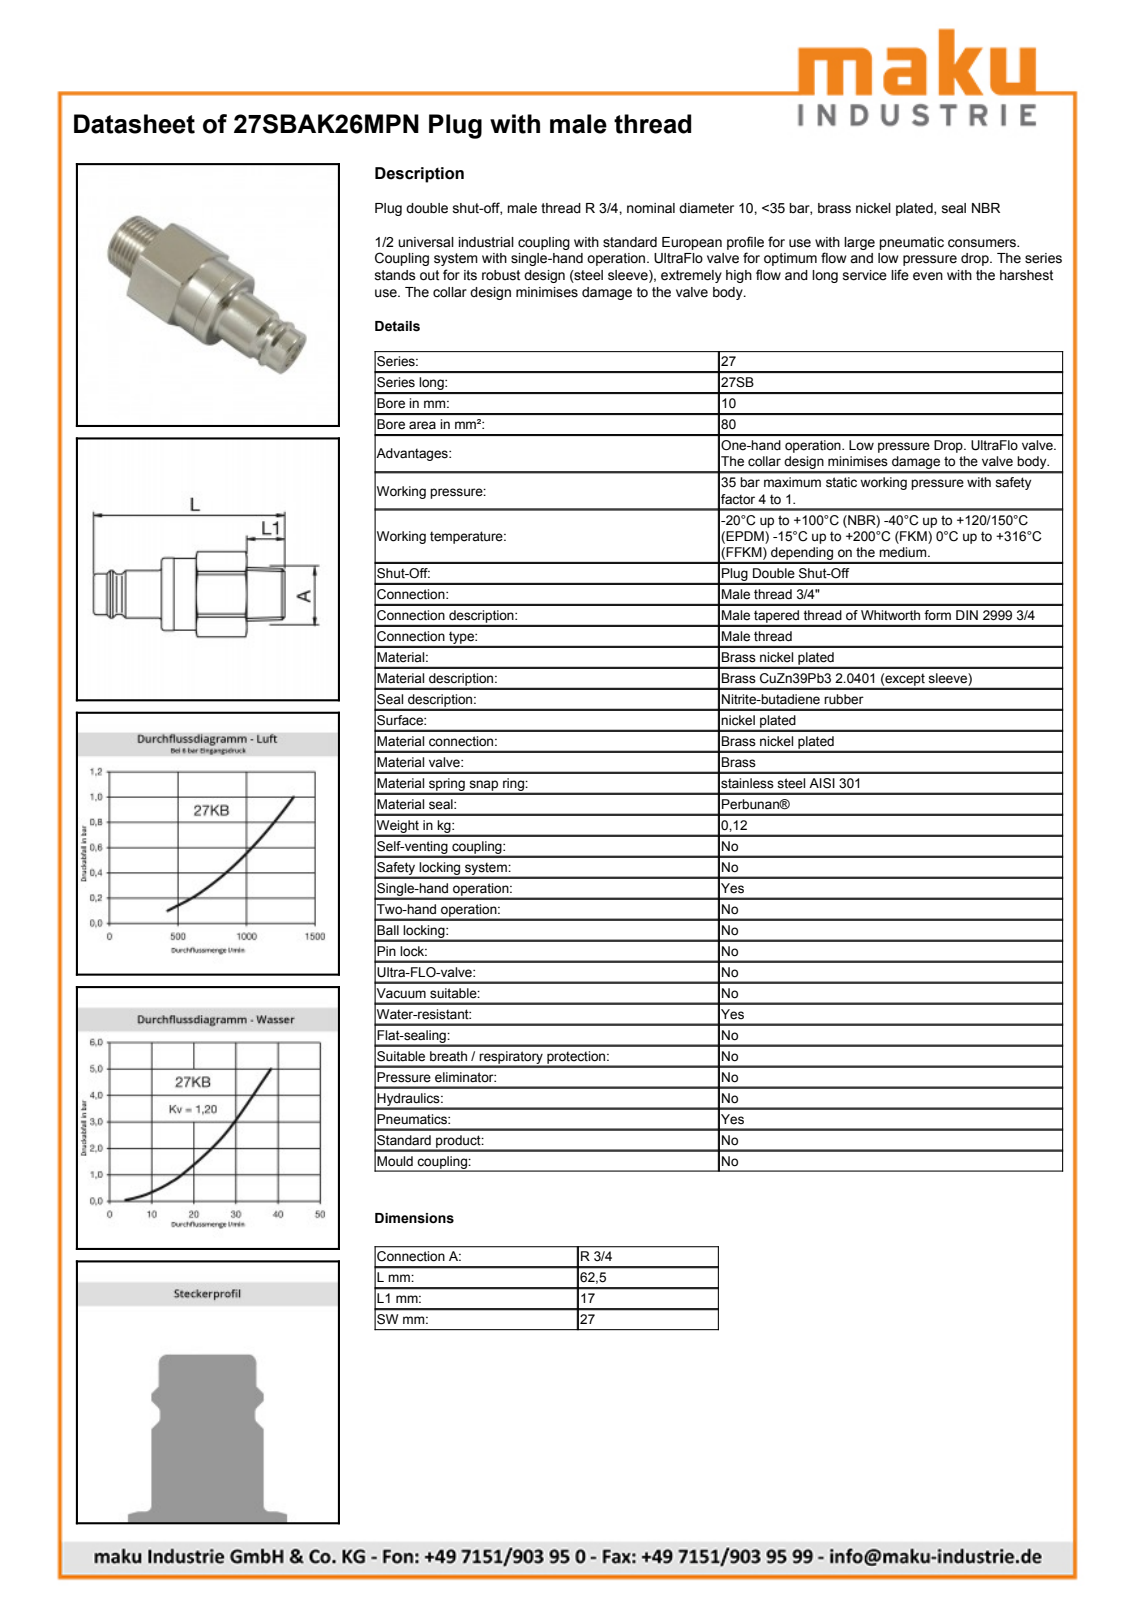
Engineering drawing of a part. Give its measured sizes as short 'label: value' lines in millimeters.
name: D112939
written by: Autodesk Inventor 2013 (AUTOMOTIVE_DESIGN)
unit: mm
bodies: 1 solid, 79 faces (32 planar, 17 cylindrical, 30 other)
size: 62.5 × 30.43 × 28.05
volume: 25 296 mm³; area: 6 208 mm²
holes: 1× ⌀19, 1× ⌀20.3
bosses: 1× ⌀23, 1× ⌀22.75, 1× ⌀18.94, 1× ⌀18.5, 1× ⌀15, 1× ⌀13, 1× ⌀12.65
rounds: 1× R15.22
face distances: 27, 27.02, 30.05, 10.95, 41, 21.5, 32.45, 62.5, 25.4, 3.9
